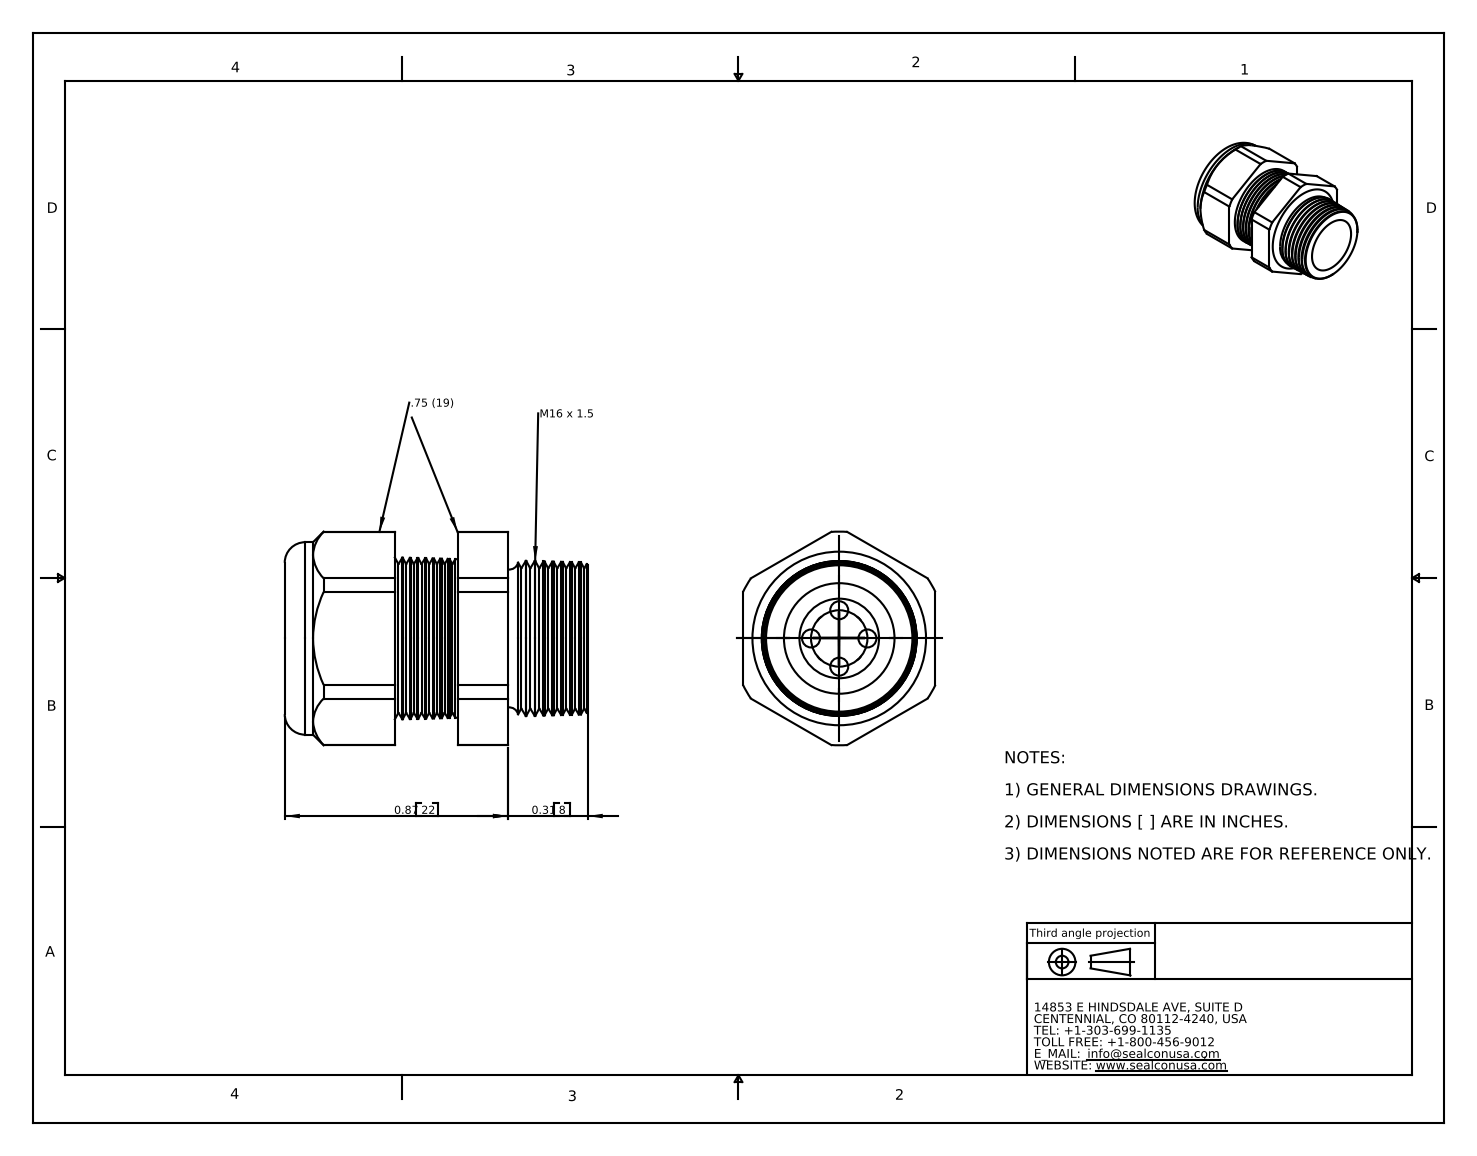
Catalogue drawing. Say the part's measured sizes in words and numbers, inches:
The part is named "CD16M8-GY". Its 3-D file was written by "SolidWorks 2007 (CONFIG_CONTROL_DESIGN)". It is 2 solids with 158 faces: 20 planar, 28 cylindrical and 110 other. Overall it measures 1.18 by 0.833 by 0.75 inches. Its volume is 0.335 cubic inches and its surface area 6.193 square inches. Round holes: 4 of diameter 0.07, 1 of diameter 0.29, 1 of diameter 0.31. Round bosses or shafts: 1 of diameter 0.75. Partial cylindrical surfaces (rounded edges, fillets, slot ends): 1 of radius 0.416. The main face-to-face distances are 0.75, 0.673, 0.75, 0.429, 0.244, 0.87, 0.441, 0.197, 1.18, 0.751. The hole center spacings are 0.11, 0.156, 0.22.
